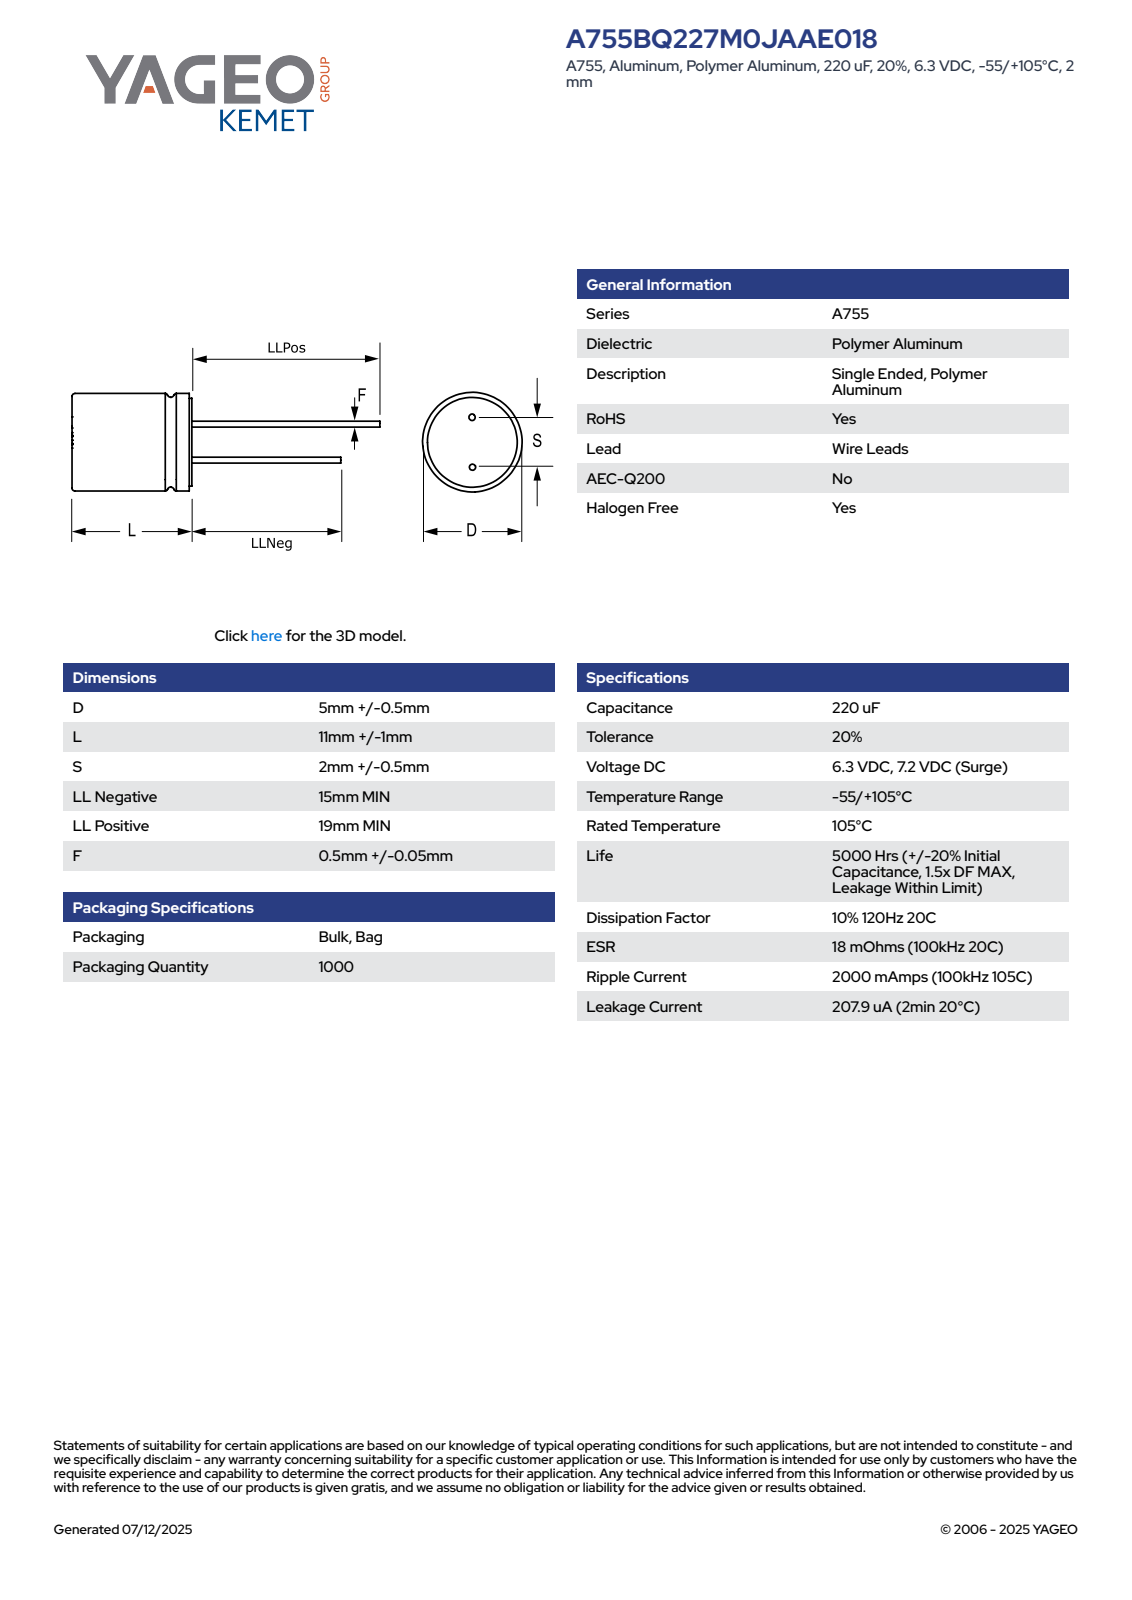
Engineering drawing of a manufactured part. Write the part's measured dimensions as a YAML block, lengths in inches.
part_name: "CAR_KP_5X11_D5.5L12S2F0.55"
step_written_by: "SolidWorks 2014 (AUTOMOTIVE_DESIGN)"
units: inches
bodies: {solids: 4, faces: 75, planar: 61, cylindrical: 8, other: 6}
overall_size: [1.22, 0.217, 0.217]
volume: 0.018
surface_area: 0.496
round_bosses_or_shafts:
  - {diameter: 0.022, count: 2}
  - {diameter: 0.217, count: 1}
face_to_face_distances: [0.472, 0.473, 1.063, 1.221, 1.063, 1.22, 0.591, 0.748, 0.157, 0.024]
